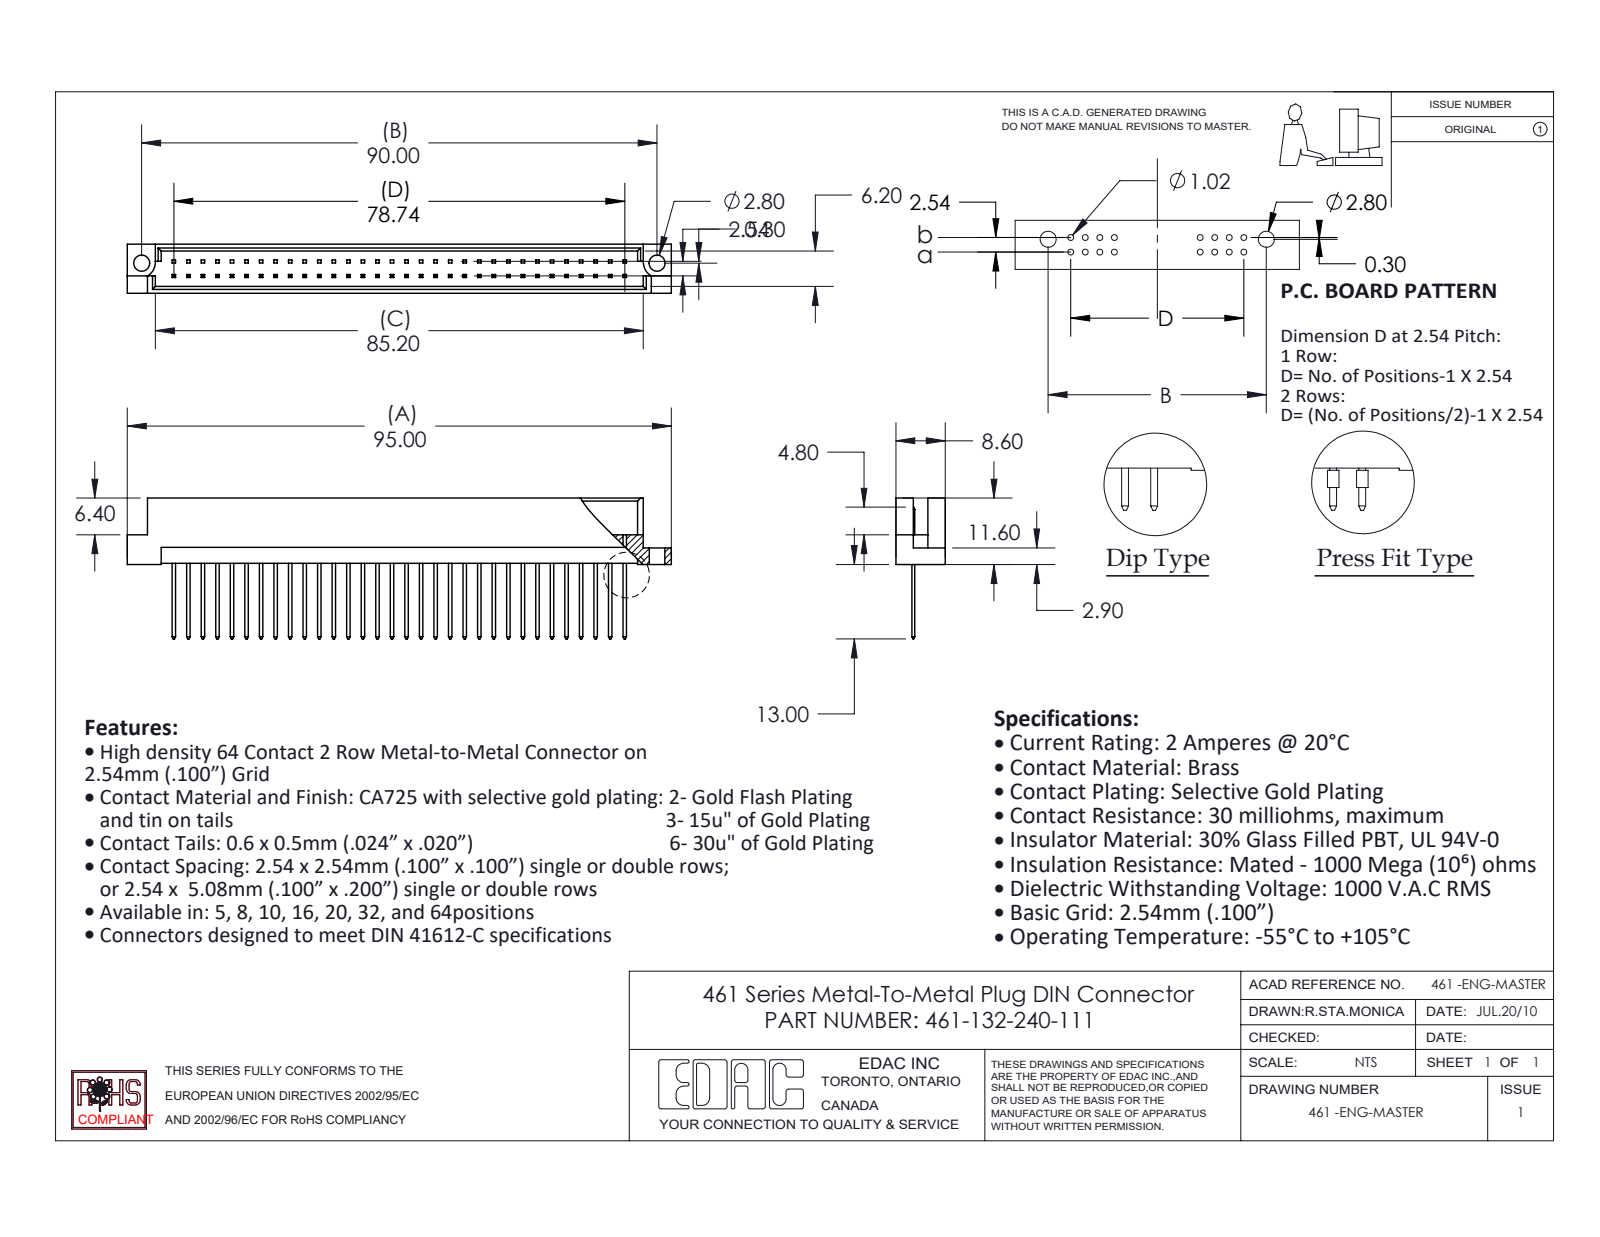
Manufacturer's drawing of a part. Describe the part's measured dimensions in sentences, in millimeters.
The part is named "461-132-240-111; 461 Part_64; 461-290_40". Its 3-D file was written by "SolidWorks 2020 (CONFIG_CONTROL_DESIGN)". It is 33 solids with 753 faces: 746 planar, 7 cylindrical and 0 other. Overall it measures 95 by 24.6 by 8.6 millimeters. Its volume is 4 874 cubic millimeters and its surface area 7 278 square millimeters. Round holes: 2 of diameter 2.8. Partial cylindrical surfaces (rounded edges, fillets, slot ends): 2 of radius 2.8. The main face-to-face distances are 1.2, 7.4, 8.6, 6.2, 3.28, 5.32, 2.08, 4.12, 2.78, 5.82. The hole center spacings are 90.
